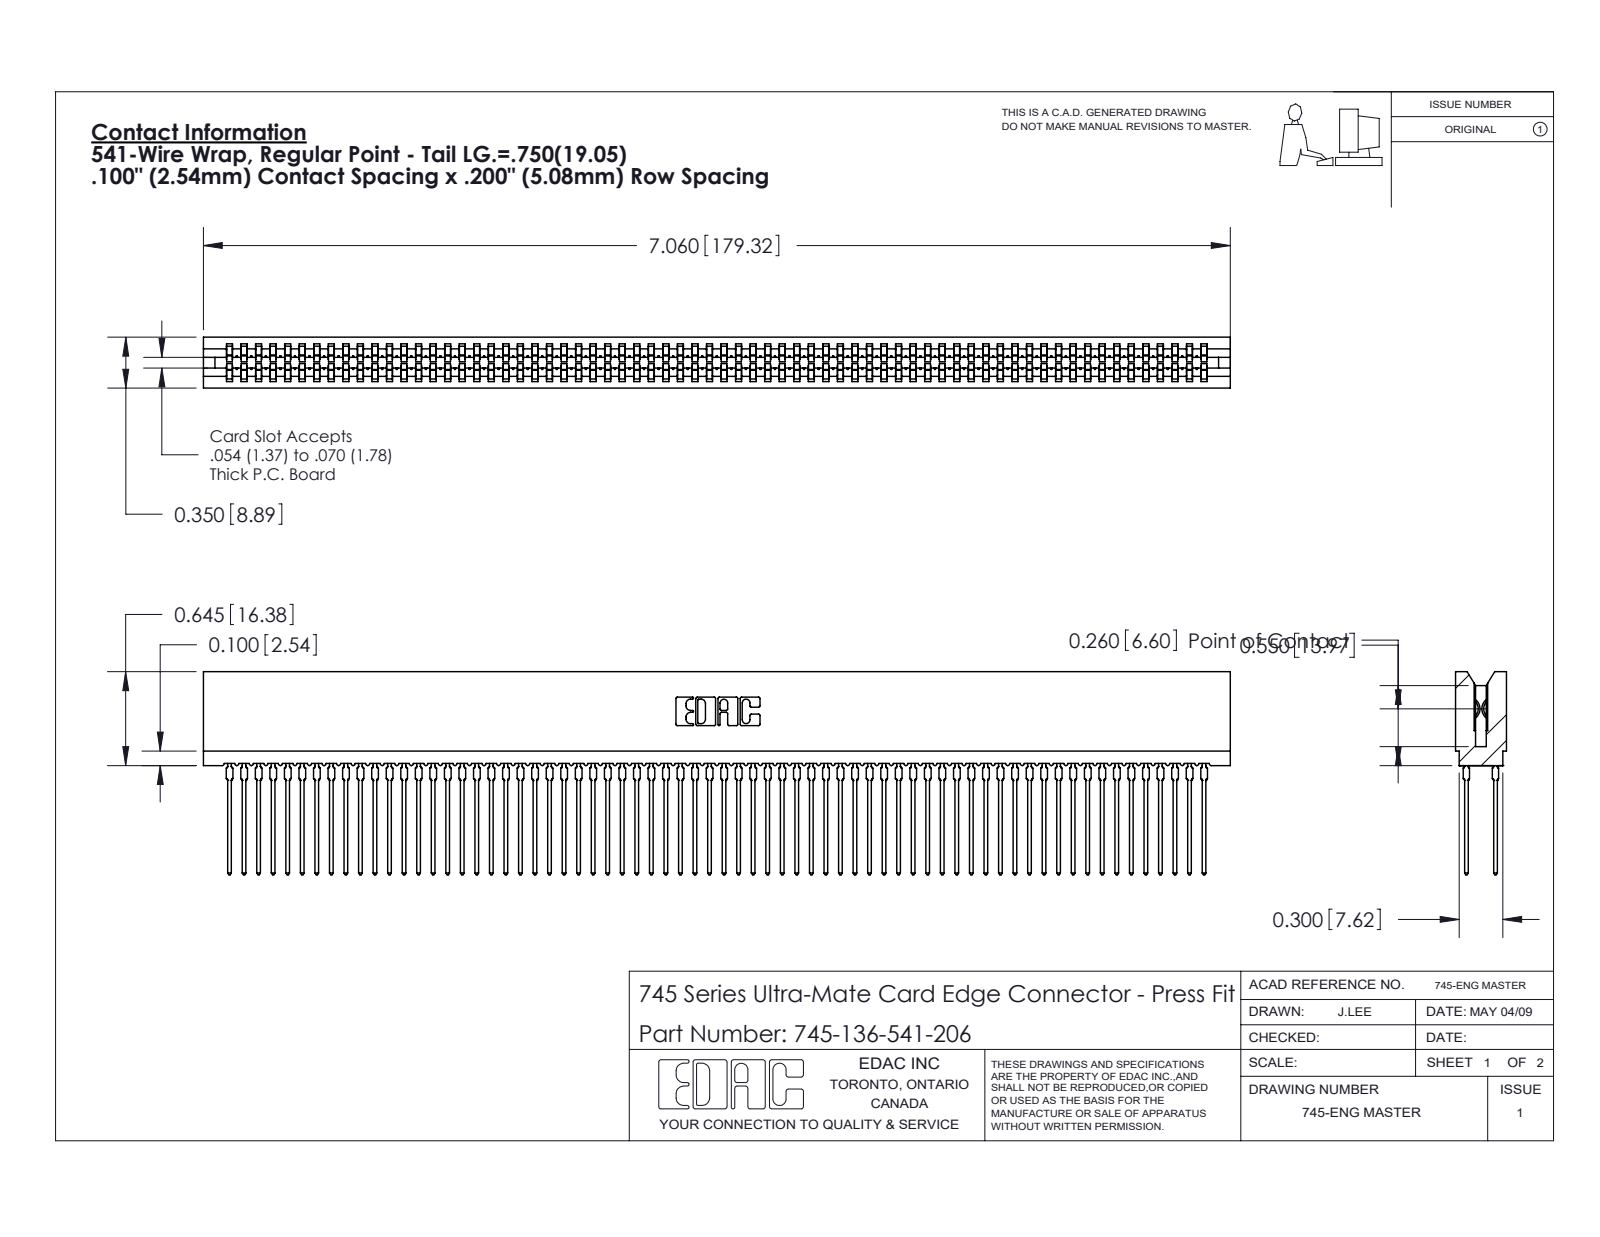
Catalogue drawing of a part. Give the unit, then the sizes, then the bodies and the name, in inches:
Units: inches
Overall size (bounding box): 7.06 × 1.396 × 0.35
Partial cylindrical surfaces — rounded edges, fillets, slot ends (radius × count): R0.021 ×272, R0.015 ×136, R0.01 ×22, R0.005 ×8, R0.011 ×8, R0.007 ×6, R0.031 ×6, R0.026 ×3
Main face-to-face distances: 0.063, 0.287, 0.2, 0.35, 0.087, 0.263, 0.025, 0.045, 0.305, 0.018
Volume: 1.015 in³ · Surface area: 57.58 in²
Bodies: 137 solids, 12268 faces (6312 planar, 2420 cylindrical, 3536 other)
Part name (STEP PRODUCT): 745-292-001_541; 745 Part_Insulator Option - 06; 745-136-541-206
STEP written by: SolidWorks 2020 (CONFIG_CONTROL_DESIGN)
